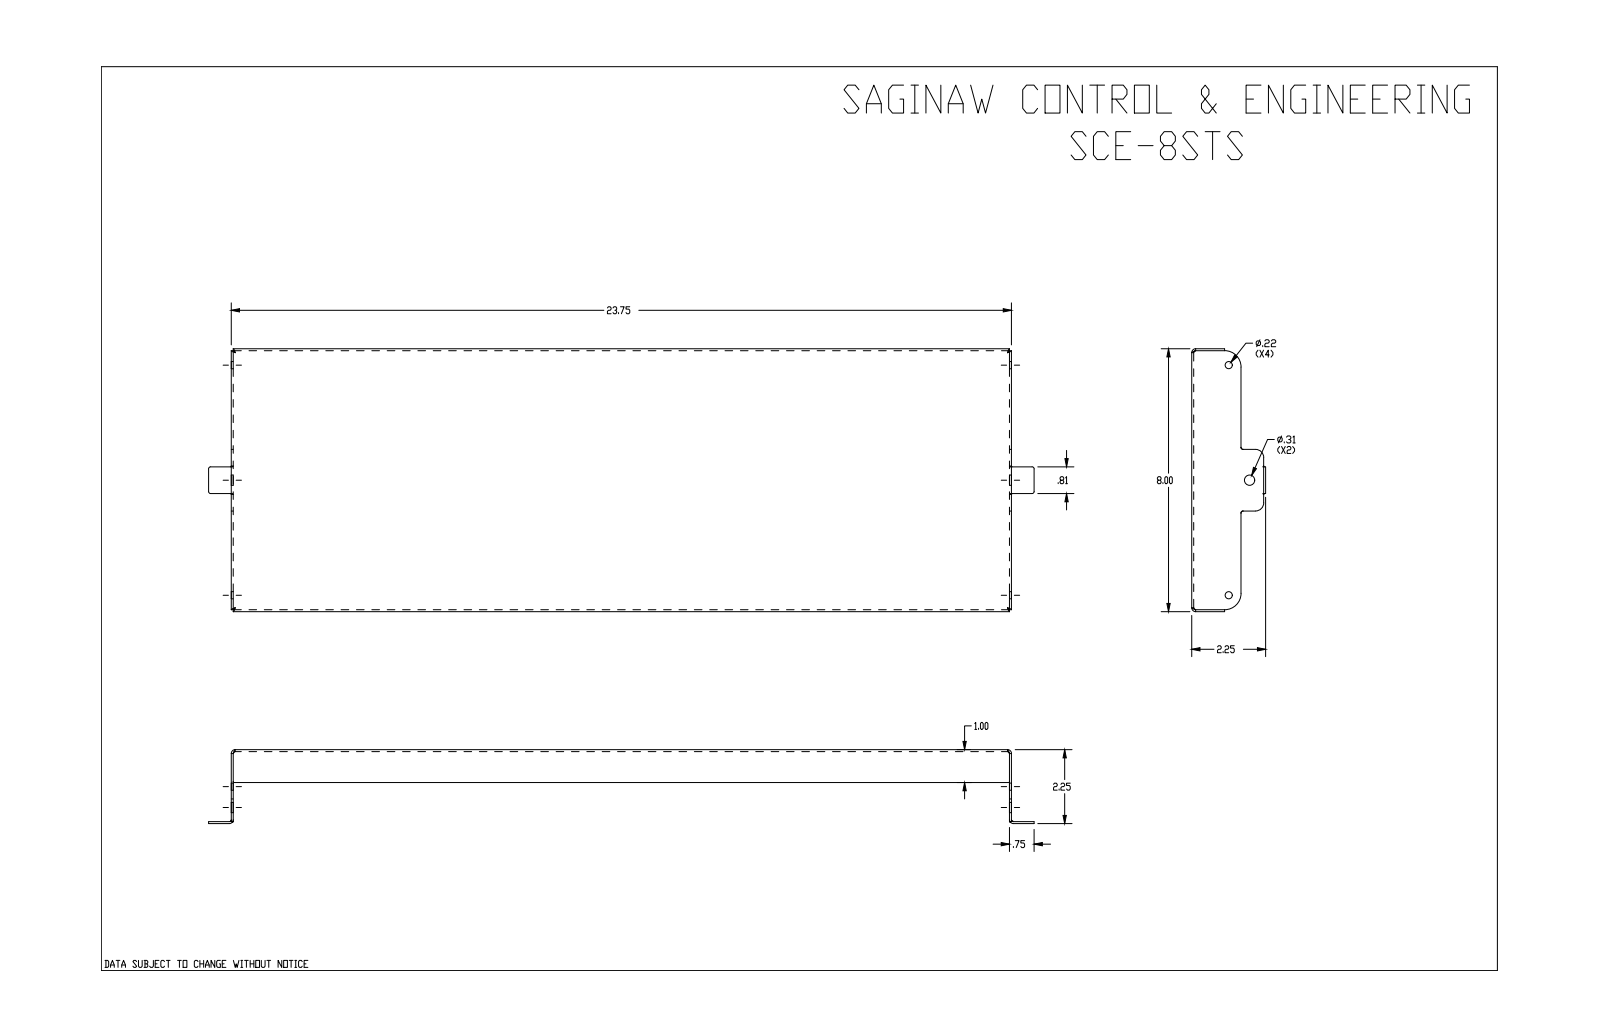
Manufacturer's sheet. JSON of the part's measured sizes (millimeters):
{"part_name": "SCE-8STS", "step_written_by": "SolidWorks 2019 (CONFIG_CONTROL_DESIGN)", "units": "millimeters", "bodies": {"solids": 1, "faces": 100, "planar": 42, "cylindrical": 38, "other": 20}, "overall_size": [638.3, 203.2, 57.2], "volume_mm3": 253500, "surface_area_mm2": 335900, "round_holes": [[5.5, 2], [8, 1]], "partial_cylinders_radius": [[1.5, 10], [3, 6], [1.6, 4], [0.8, 2], [6.4, 2], [12.7, 2]], "face_to_face_distances": [1.5, 201.7, 601.7, 200.2, 203.2, 600.2, 603.3, 23.9, 25.4, 55.6], "hole_center_spacings": [90.3, 177.8]}
